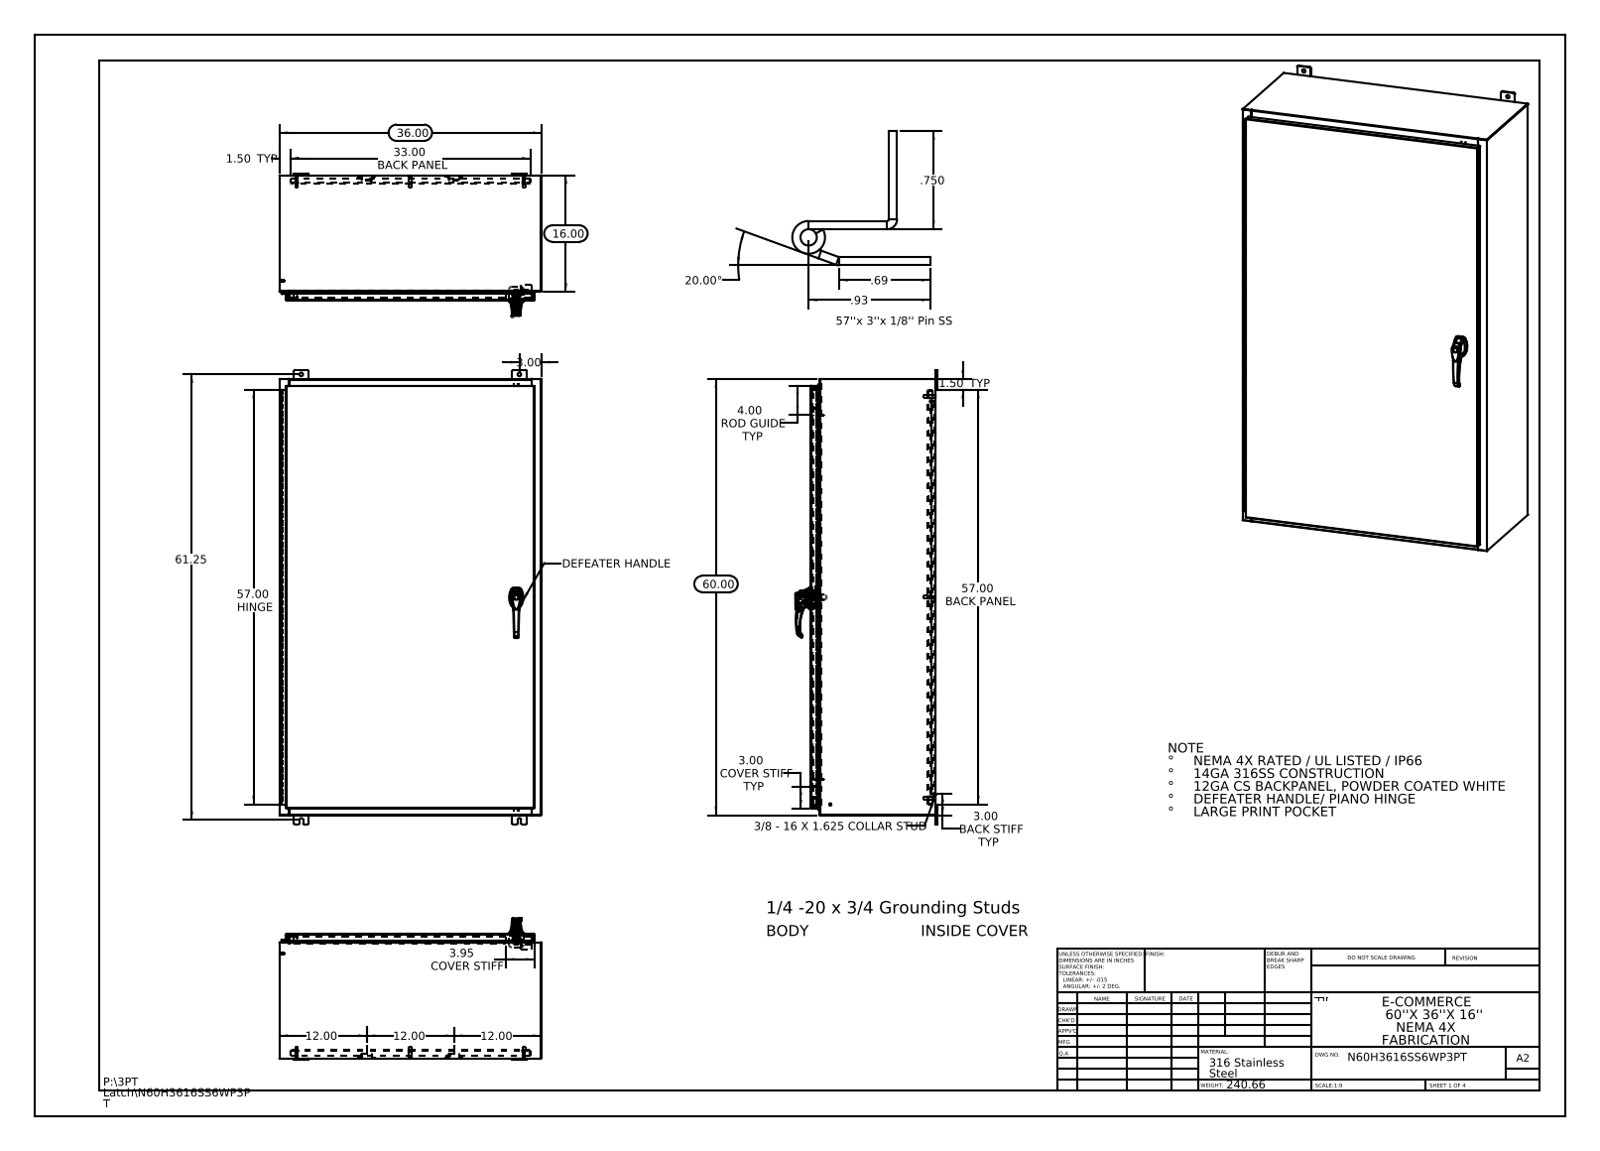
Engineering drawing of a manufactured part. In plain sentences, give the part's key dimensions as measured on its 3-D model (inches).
The part is named "297025; N60H3616SS6WP3PT Enclosure Stiffener; 033060_032151; Quarter-20 CD Stud (+8 more)". Its 3-D file was written by "SolidWorks 2013 (CONFIG_CONTROL_DESIGN)". It is 51 solids with 3688 faces: 1453 planar, 1449 cylindrical and 786 other. Overall it measures 62.5 by 36 by 19.495 inches. Its volume is 855.6 cubic inches and its surface area 21 358 square inches. Round holes: 12 of diameter 0.5, 10 of diameter 0.25, 3 of diameter 0.138, 3 of diameter 0.161, 2 of diameter 0.079, 2 of diameter 0.203, 2 of diameter 0.313, 2 of diameter 0.437, 1 of diameter 0.125, 1 of diameter 0.125, 1 of diameter 0.197, 1 of diameter 0.276. Round bosses or shafts: 10 of diameter 0.157, 10 of diameter 0.14, 8 of diameter 0.625, 8 of diameter 0.375, 8 of diameter 0.33, 3 of diameter 0.315, 3 of diameter 0.236, 1 of diameter 1.181. Partial cylindrical surfaces (rounded edges, fillets, slot ends): 37 of radius 0.118, 34 of radius 0.013, 33 of radius 0.006, 28 of radius 0.088, 24 of radius 0.19, 15 of radius 0.039, 12 of radius 0.028, 6 of radius 0.008. The main face-to-face distances are 0.075, 17.126, 17.051, 0.104, 17.201, 35.925, 1, 16.126, 1.075, 16.051. The hole center spacings are 23.354, 25.662, 27.625, 41.709, 57.417, 30.975, 31.25, 55.25.
